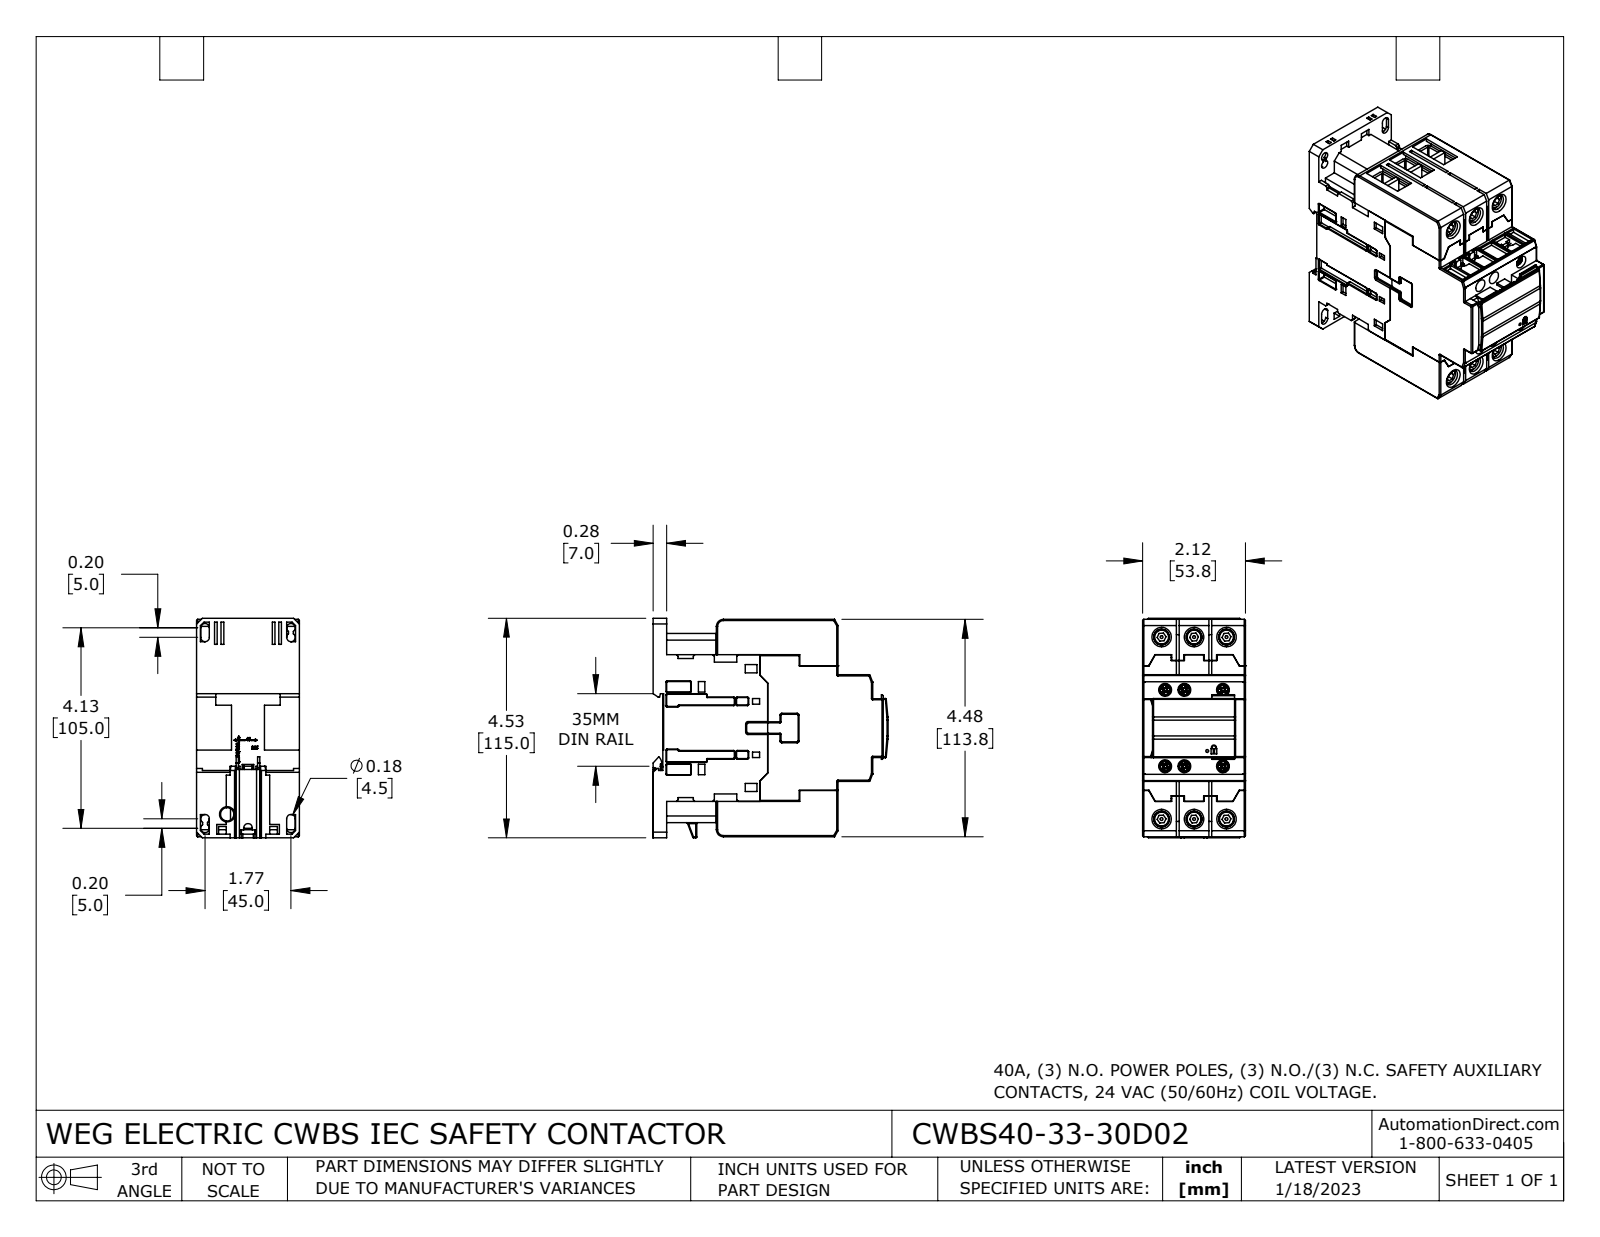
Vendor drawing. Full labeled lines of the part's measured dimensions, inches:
Part name (STEP PRODUCT): CWBS40-33-30D02
STEP written by: SolidWorks 2021 (CONFIG_CONTROL_DESIGN)
Units: inches
Bodies: 37 solids, 2637 faces (1669 planar, 550 cylindrical, 418 other)
Overall size (bounding box): 4.846 × 4.528 × 2.118
Volume: 33.67 in³ · Surface area: 209.3 in²
Round holes (diameter × count): ⌀0.124 ×6, ⌀0.197 ×6, ⌀0.264 ×6, ⌀0.323 ×6, ⌀0.177 ×4, ⌀0.125 ×2, ⌀0.276 ×2, ⌀0.059 ×1
Round bosses / shafts (diameter × count): ⌀0.343 ×6, ⌀0.236 ×6, ⌀0.135 ×6
Partial cylindrical surfaces — rounded edges, fillets, slot ends (radius × count): R0.02 ×89, R0.012 ×69, R0.004 ×48, R0.024 ×42, R0.079 ×18, R0.089 ×5, R0.039 ×3, R0.059 ×3
Main face-to-face distances: 0.059, 2.118, 0.669, 0.728, 3.024, 3.752, 0.108, 0.217, 3.811, 0.098
Hole centre spacings: 0.669, 1.091, 1.241, 1.669, 2.665, 2.73, 2.949, 3.811
